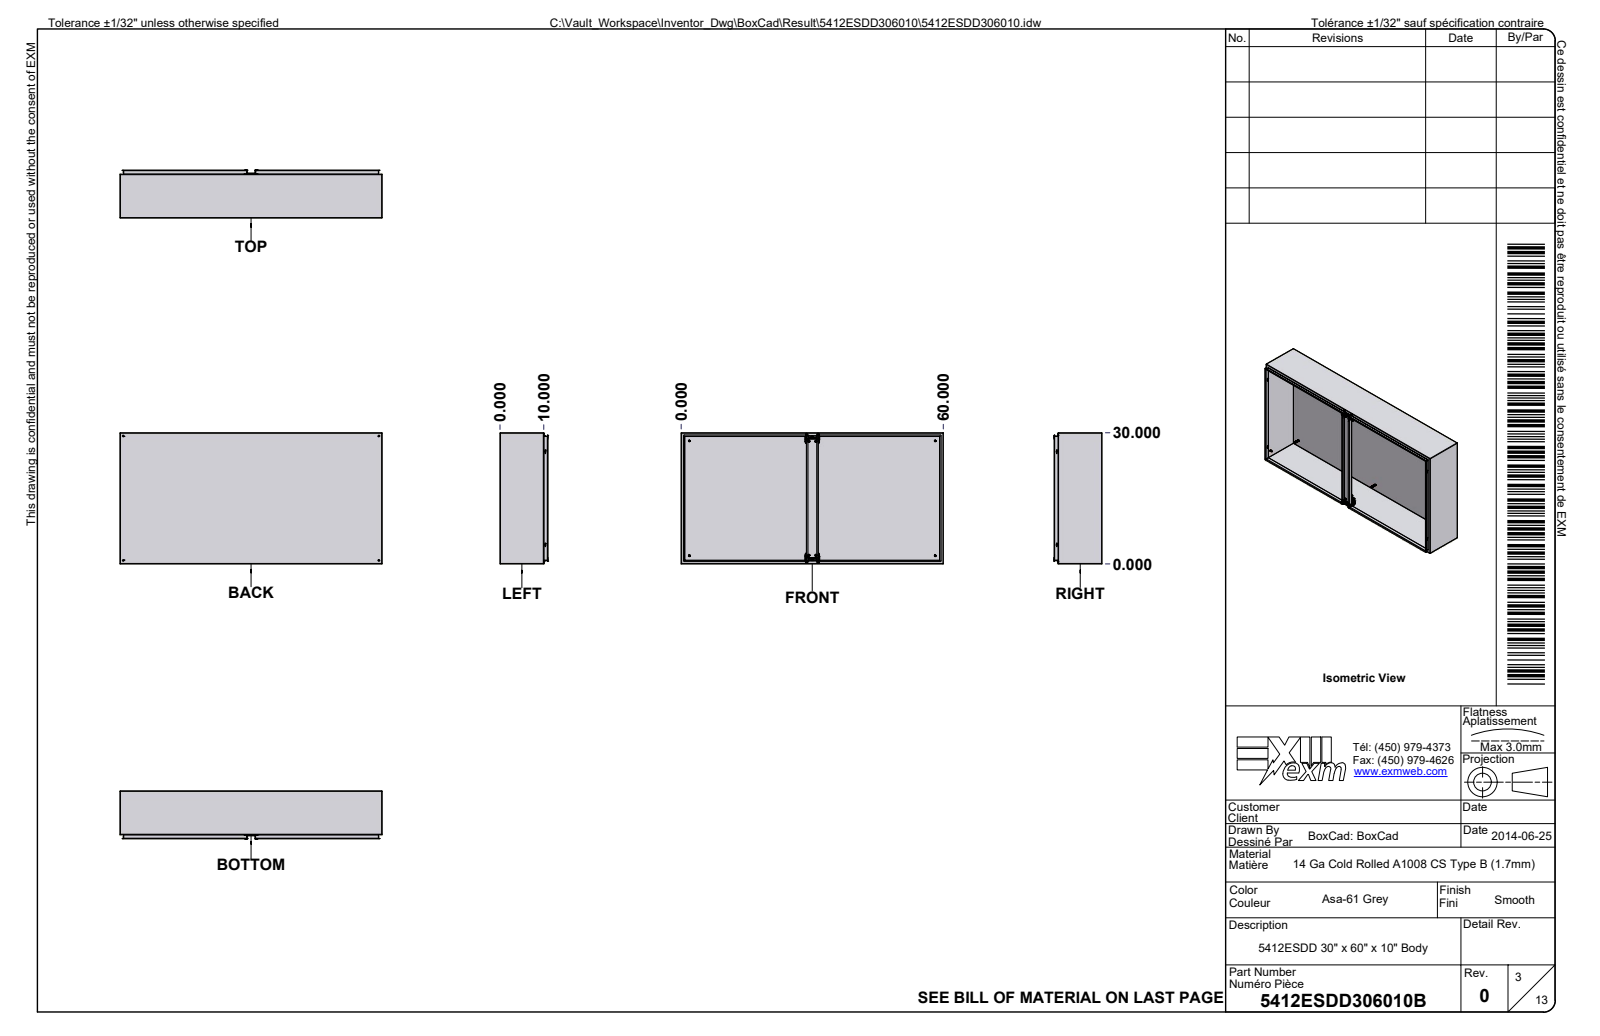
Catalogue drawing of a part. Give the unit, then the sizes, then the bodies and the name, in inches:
Units: inches
Overall size (bounding box): 60.036 × 30 × 11.295
Round holes (diameter × count): ⌀0.165 ×104, ⌀0.03 ×15, ⌀0.201 ×14, ⌀0.315 ×14, ⌀0.043 ×12, ⌀0.311 ×12, ⌀0.197 ×8, ⌀0.268 ×8, ⌀0.287 ×8, ⌀0.236 ×6, ⌀0.24 ×6, ⌀0.27 ×6
Round bosses / shafts (diameter × count): ⌀0.237 ×104, ⌀0.232 ×25, ⌀0.03 ×15, ⌀0.472 ×12, ⌀0.039 ×12, ⌀0.374 ×8, ⌀0.177 ×8, ⌀0.717 ×6
Partial cylindrical surfaces — rounded edges, fillets, slot ends (radius × count): R0.02 ×876, R0.039 ×469, R0.008 ×340, R0.01 ×266, R0.012 ×84, R0.079 ×66, R0.118 ×62, R0.03 ×60
Main face-to-face distances: 0.068, 11.052, 10.983, 11.12, 0.942, 0.874, 10.109, 10.178, 0.105, 1.047
Hole centre spacings: 2.625, 26.855, 27.94, 29.476, 30.565, 21.303, 0.35, 0.499
Volume: 623 in³ · Surface area: 16 320 in²
Bodies: 155 solids, 25520 faces (8086 planar, 6944 cylindrical, 10490 other)
Part name (STEP PRODUCT): 5412ESDD306010; 5412ESDD306010B; 5412ESDD306010B-P; 5412ESDD306010CP-P (+8 more)
STEP written by: Autodesk Inventor 2024 (AUTOMOTIVE_DESIGN)
